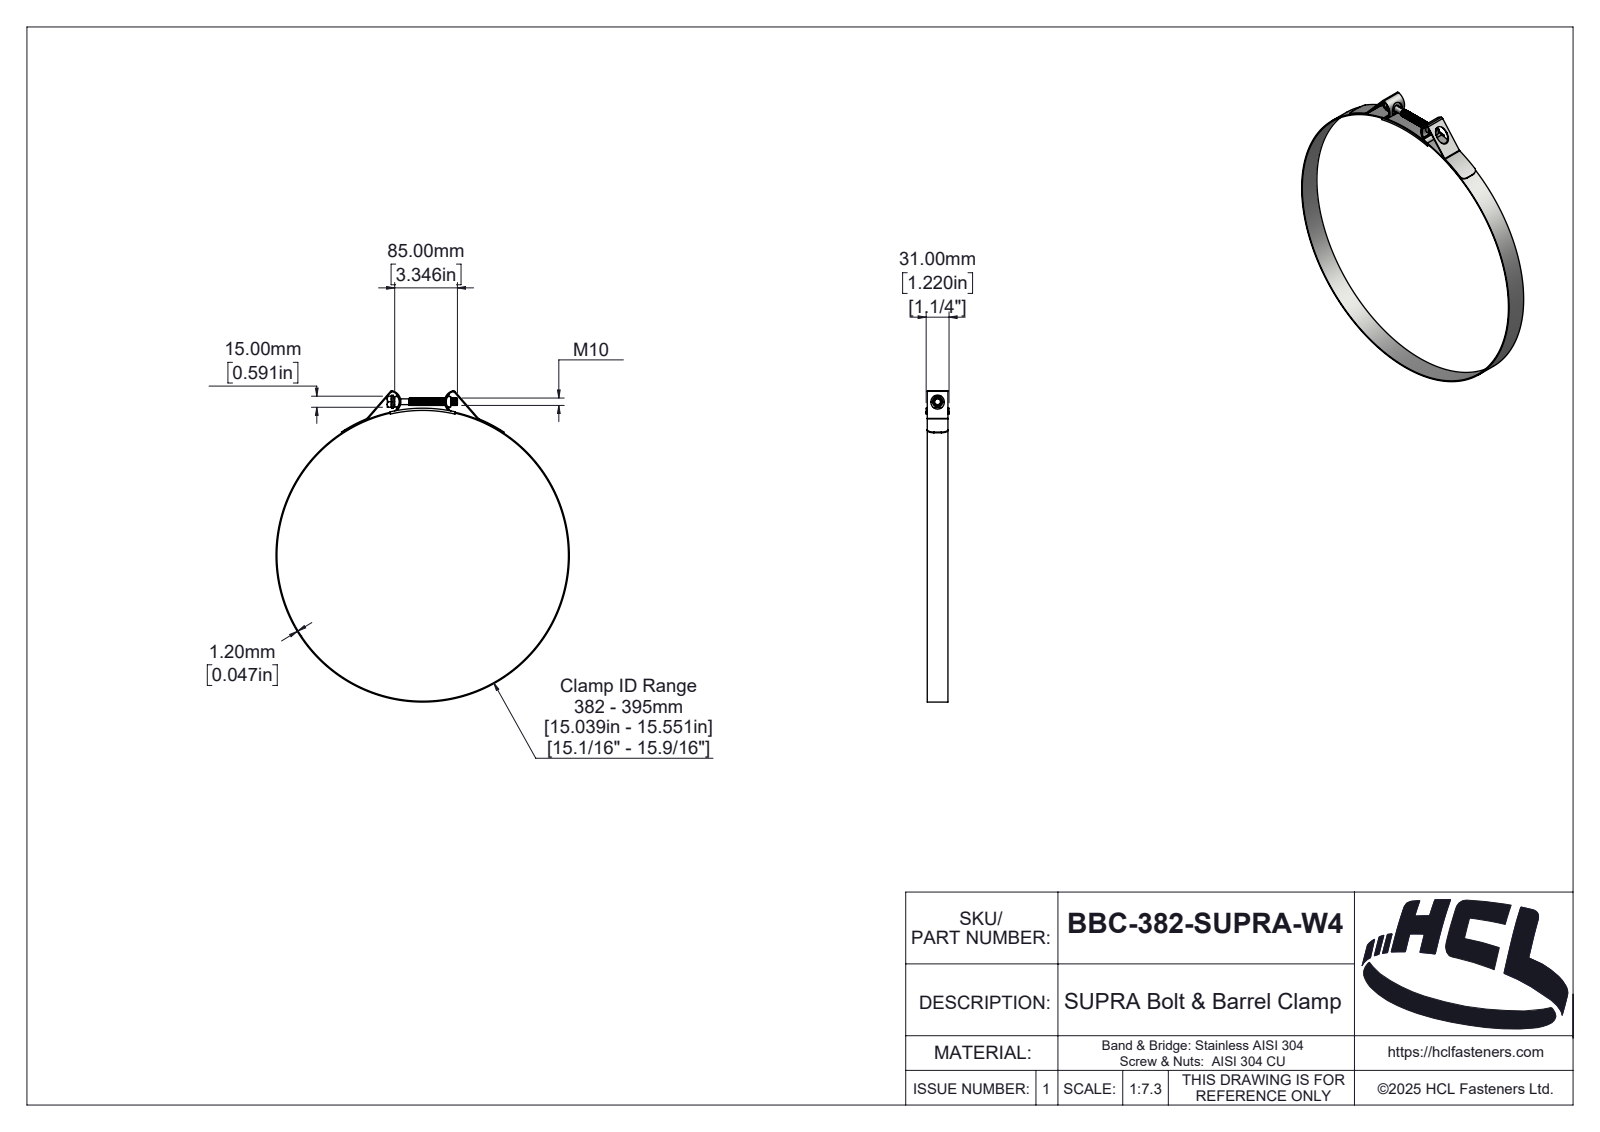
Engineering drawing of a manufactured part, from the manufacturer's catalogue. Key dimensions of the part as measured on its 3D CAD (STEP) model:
Part name (STEP PRODUCT): BBC-382-SUPRA-W4
STEP written by: SolidWorks 2025 (AUTOMOTIVE_DESIGN)
Units: millimetres
Bodies: 5 solids, 378 faces (50 planar, 241 cylindrical, 87 other)
Overall size (bounding box): 421.66 × 397.4 × 31
Volume: 59 145 mm³ · Surface area: 94 768 mm²
Round holes (diameter × count): ⌀395 ×1
Round bosses / shafts (diameter × count): ⌀397.4 ×1, ⌀17.32 ×1, ⌀14 ×1, ⌀10 ×1, ⌀7.8 ×1
Partial cylindrical surfaces — rounded edges, fillets, slot ends (radius × count): R1 ×4, R1.3 ×2, R2 ×2, R2.5 ×2, R3.2 ×2, R9 ×2, R13.03 ×2, R14.03 ×2
Main face-to-face distances: 1.2, 28, 1.5, 29.5, 29.8, 28.3, 31, 28.6, 83.32, 12.5
